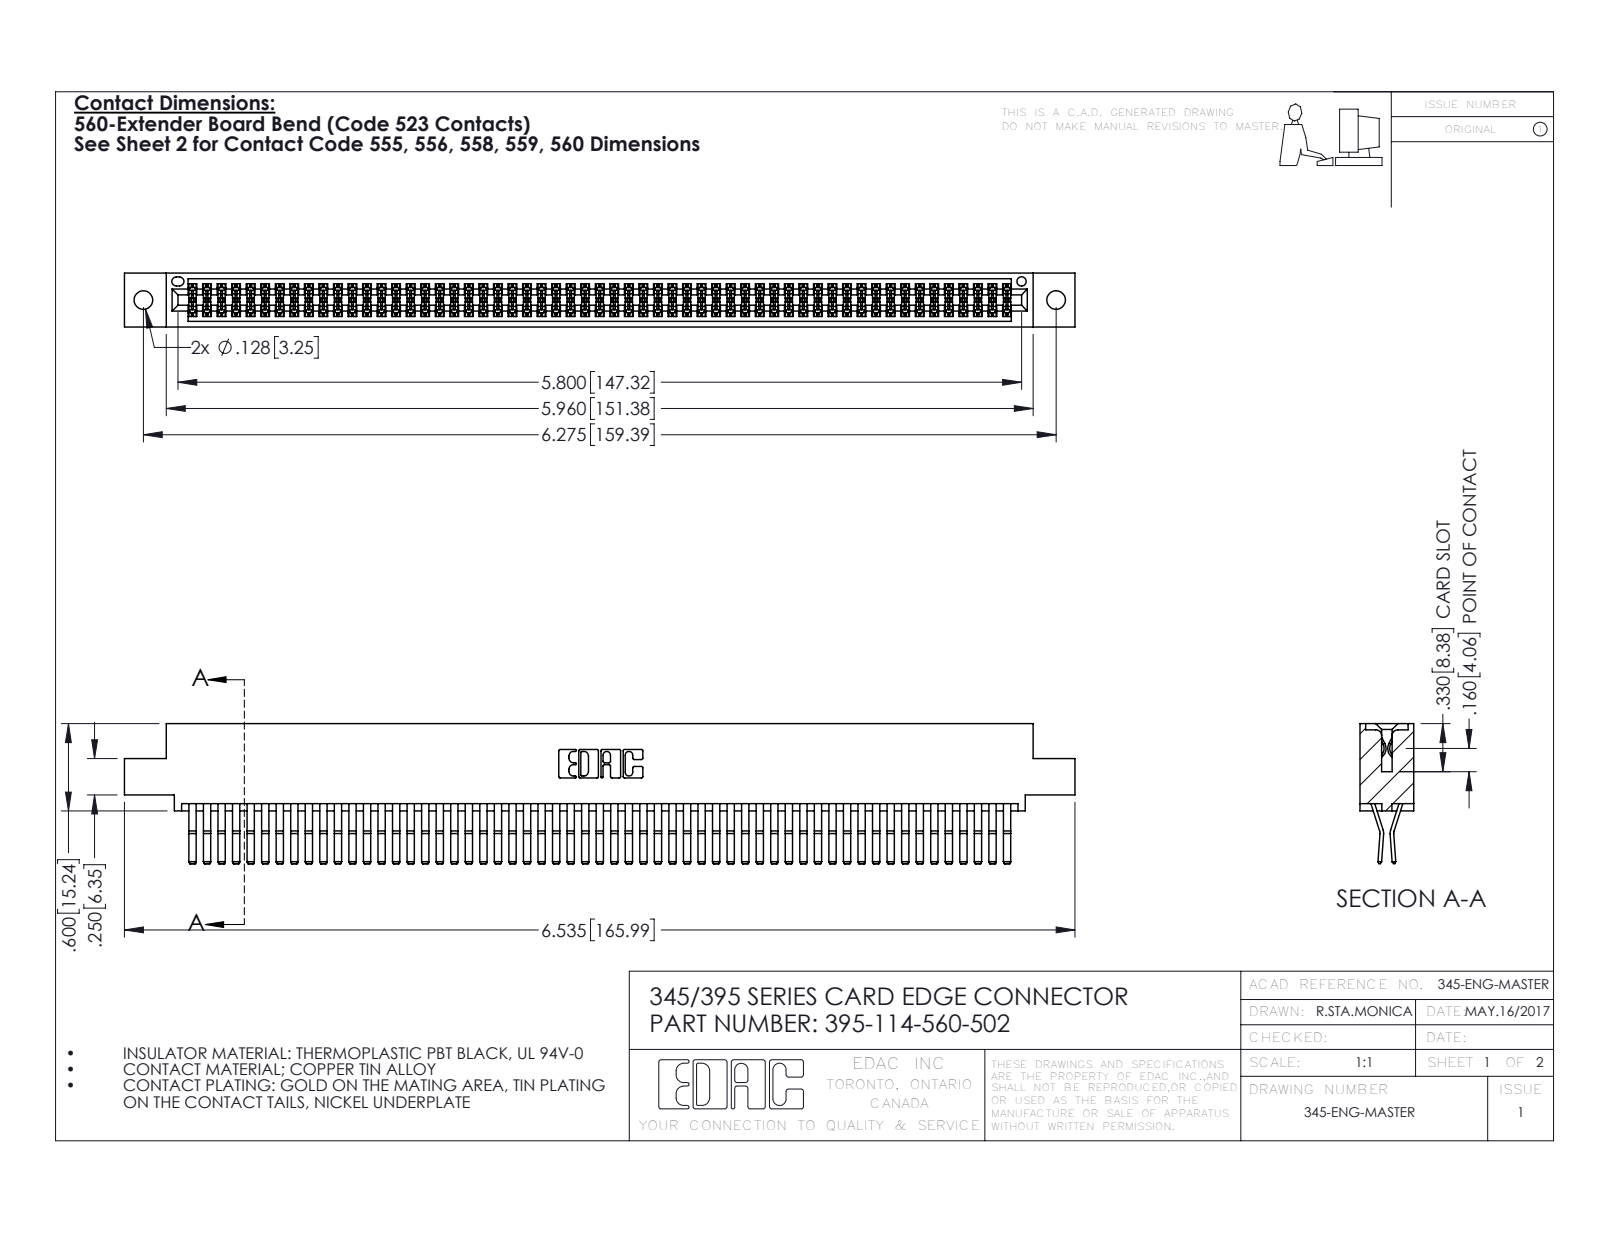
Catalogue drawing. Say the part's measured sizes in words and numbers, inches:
The part is named "345-292-001_560 Tail; 395-114-560-502; 345 Part_0.110 Offset - 0.128 Dia". Its 3-D file was written by "SolidWorks 2016 (CONFIG_CONTROL_DESIGN)". It is 115 solids with 6058 faces: 3846 planar, 2212 cylindrical and 0 other. Overall it measures 6.535 by 0.962 by 0.37 inches. Its volume is 1.031 cubic inches and its surface area 41.87 square inches. Round holes: 2 of diameter 0.128, 1 of diameter 0.064. Partial cylindrical surfaces (rounded edges, fillets, slot ends): 172 of radius 0.006, 22 of radius 0.01, 6 of radius 0.007, 6 of radius 0.031, 3 of radius 0.026, 2 of radius 0.01, 2 of radius 0.014, 2 of radius 0.019. The main face-to-face distances are 0.025, 0.298, 0.072, 0.37, 0.2, 0.098, 0.272, 0.225, 0.175, 0.149. The hole center spacings are 0.27, 6.039, 6.275.
